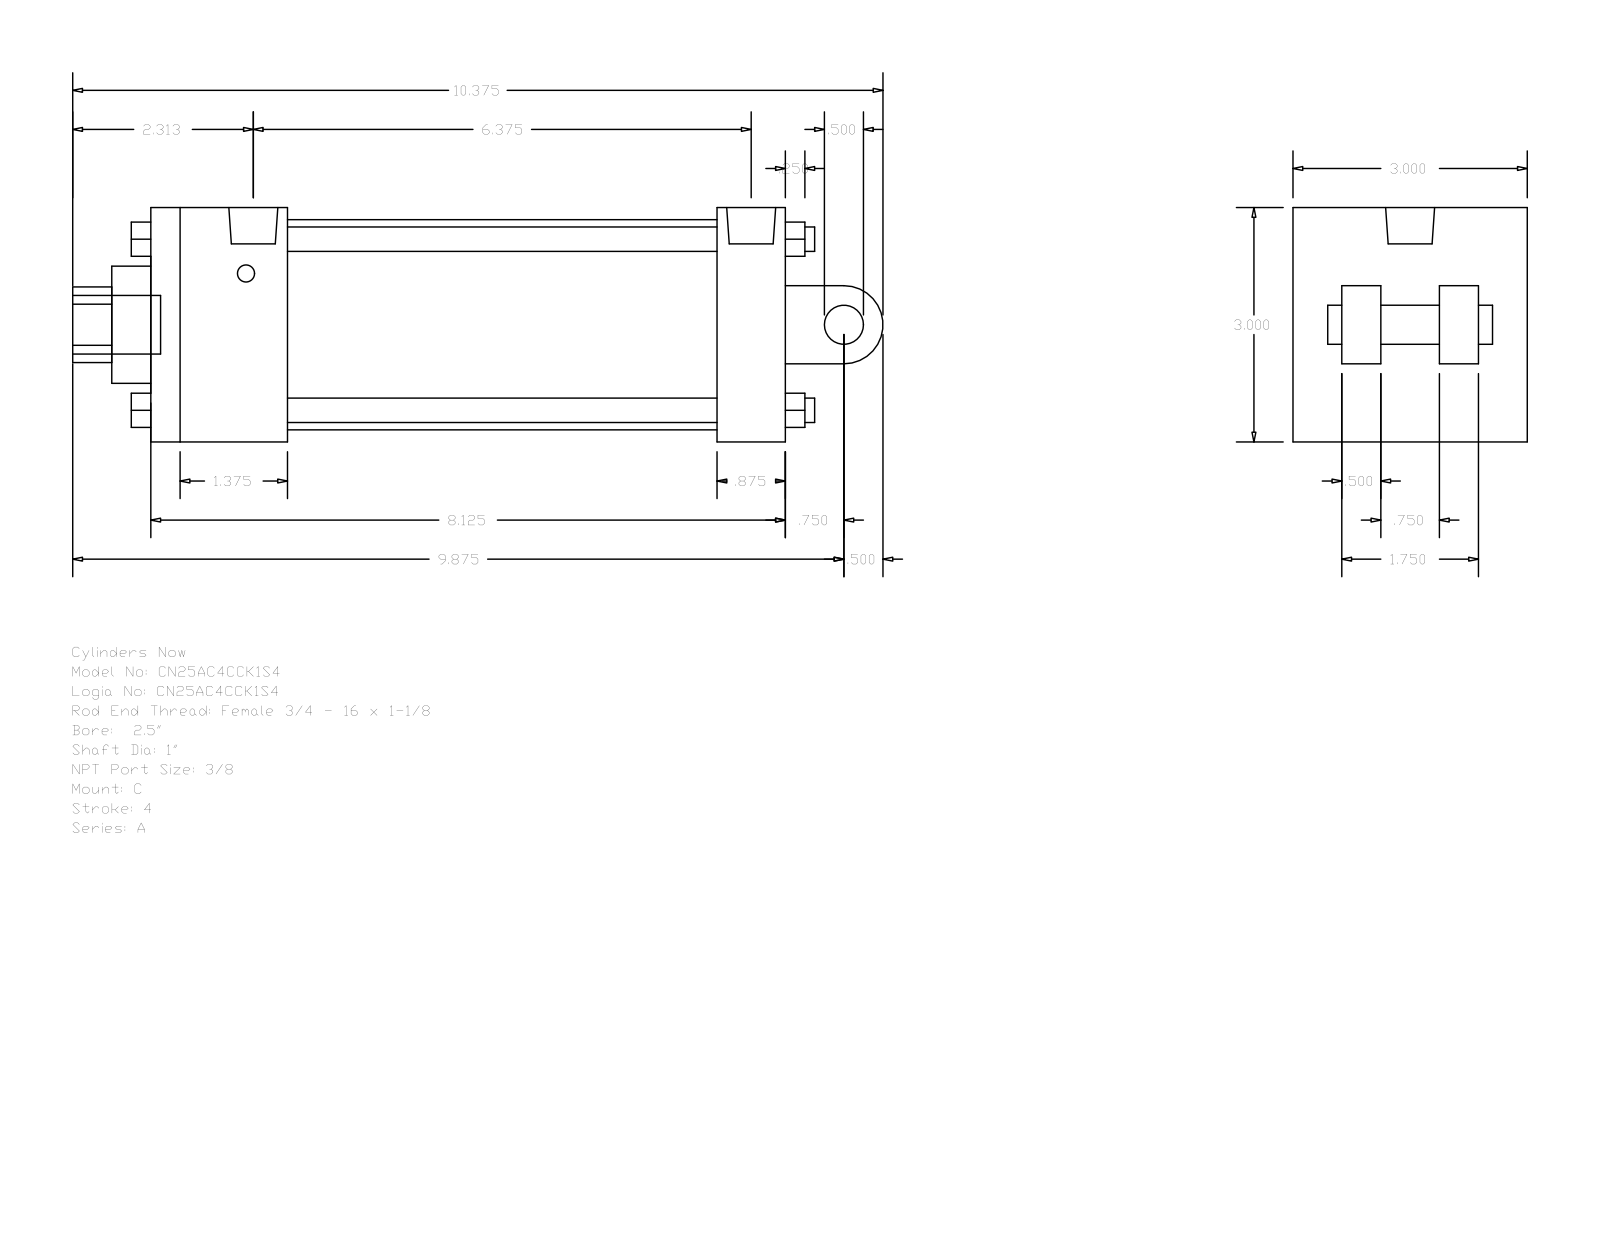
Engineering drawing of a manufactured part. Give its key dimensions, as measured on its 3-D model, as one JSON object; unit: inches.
{"part_name": "A_C__0250_1", "step_written_by": "GSSL Pune (CONFIG_CONTROL_DESIGN)", "units": "inches", "bodies": {"solids": 0, "faces": 135, "planar": 102, "cylindrical": 33, "other": 0}, "overall_size": [10.375, 3, 3], "round_holes": [[0.219, 2], [0.627, 1], [1, 1], [1.5, 1], [2.69, 1]], "round_bosses_or_shafts": [[0.313, 4], [0.219, 2], [0.75, 1], [0.627, 1], [0.5, 1]], "partial_cylinders_radius": [[0.484, 1], [0.5, 1]], "face_to_face_distances": [3, 8.125, 0.5, 1.75, 7.25, 5.5, 6.375, 0.875, 0.625, 1], "hole_center_spacings": [0.094]}
